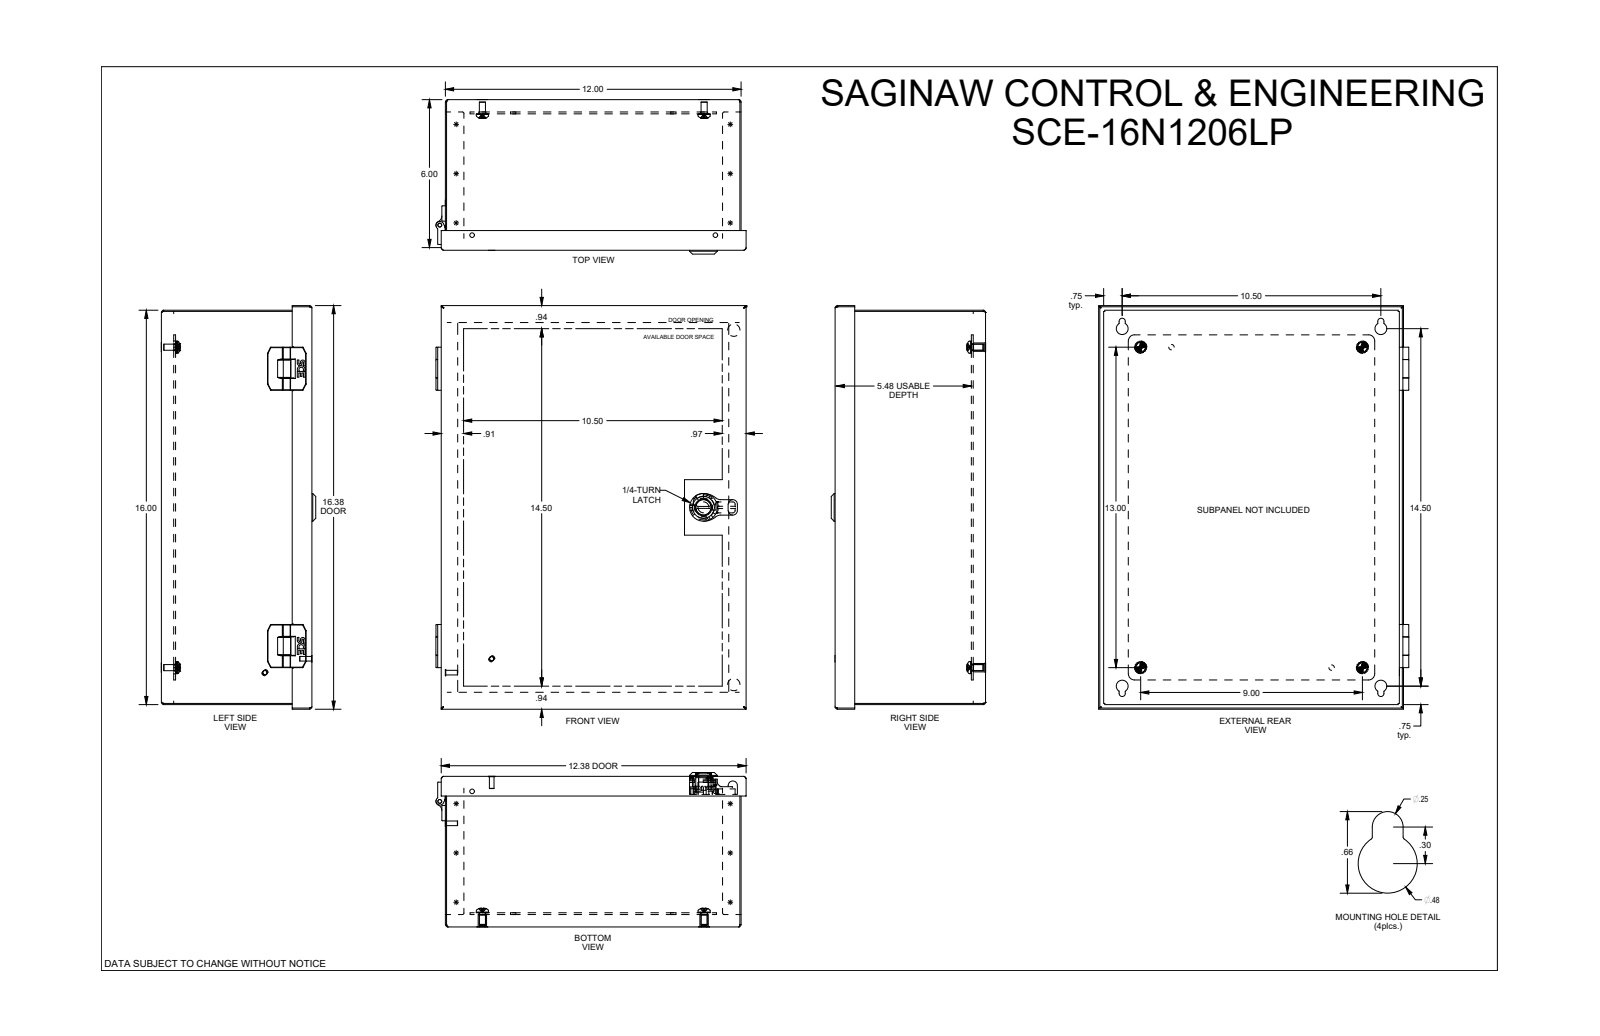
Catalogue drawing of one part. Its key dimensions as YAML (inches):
part_name: "SCE-16N1206LP"
step_written_by: "SolidWorks 2019 (AUTOMOTIVE_DESIGN)"
units: inches
bodies: {solids: 31, faces: 1545, planar: 578, cylindrical: 643, other: 324}
overall_size: [16.375, 12.593, 6.267]
volume: 59.74
surface_area: 1913
round_holes:
  - {diameter: 0.17, count: 4}
  - {diameter: 0.25, count: 4}
  - {diameter: 0.281, count: 4}
  - {diameter: 0.329, count: 4}
  - {diameter: 0.343, count: 4}
  - {diameter: 0.48, count: 4}
  - {diameter: 0.193, count: 3}
  - {diameter: 0.187, count: 2}
  - {diameter: 0.218, count: 2}
  - {diameter: 0.158, count: 1}
  - {diameter: 0.44, count: 1}
  - {diameter: 0.635, count: 1}
round_bosses_or_shafts:
  - {diameter: 0.492, count: 4}
  - {diameter: 0.479, count: 4}
  - {diameter: 0.341, count: 4}
  - {diameter: 0.248, count: 4}
  - {diameter: 0.237, count: 4}
  - {diameter: 0.16, count: 4}
  - {diameter: 0.5, count: 2}
  - {diameter: 0.323, count: 2}
partial_cylinders:
  - {radius: 0.01, count: 253}
  - {radius: 0.02, count: 95}
  - {radius: 0.06, count: 25}
  - {radius: 0.015, count: 24}
  - {radius: 0.025, count: 24}
  - {radius: 0.055, count: 6}
  - {radius: 0.25, count: 6}
  - {radius: 0.125, count: 4}
face_to_face_distances: [0.06, 6.047, 5.987, 6.107, 11.94, 0.5, 0.44, 0.575, 0.515, 5.472]
hole_center_spacings: [1.061, 1.089, 1.091, 9.779, 11.25, 13.77, 16.856, 11.25]
